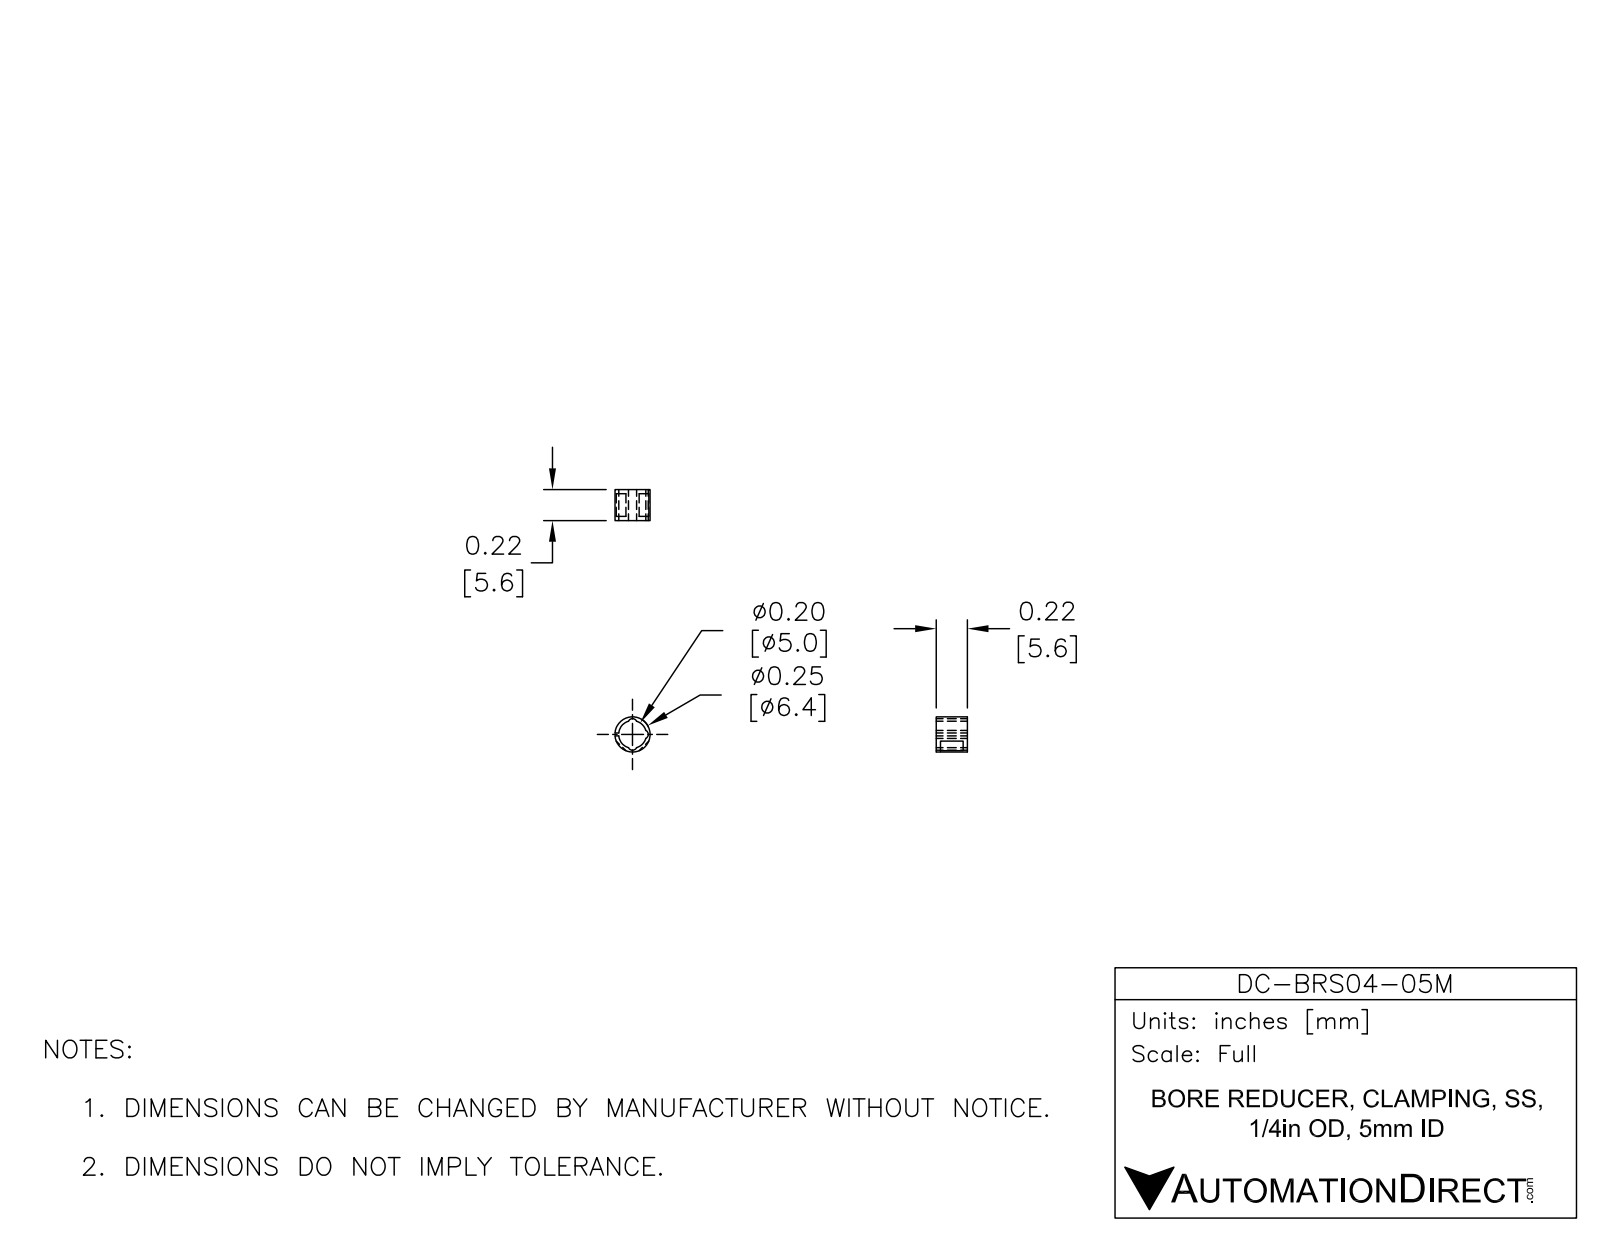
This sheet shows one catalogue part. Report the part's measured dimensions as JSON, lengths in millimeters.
{"part_name": "DC-BRS04-05M", "step_written_by": "SolidWorks 2015 (AUTOMOTIVE_DESIGN)", "units": "millimeters", "bodies": {"solids": 1, "faces": 21, "planar": 10, "cylindrical": 11, "other": 0}, "overall_size": [6.35, 6.34, 5.61], "volume_mm3": 56, "surface_area_mm2": 230, "round_bosses_or_shafts": [[6.35, 1]], "partial_cylinders_radius": [[0.81, 3], [2.5, 1]], "face_to_face_distances": [5.62, 0.5, 0.77, 4.85, 4.08]}
